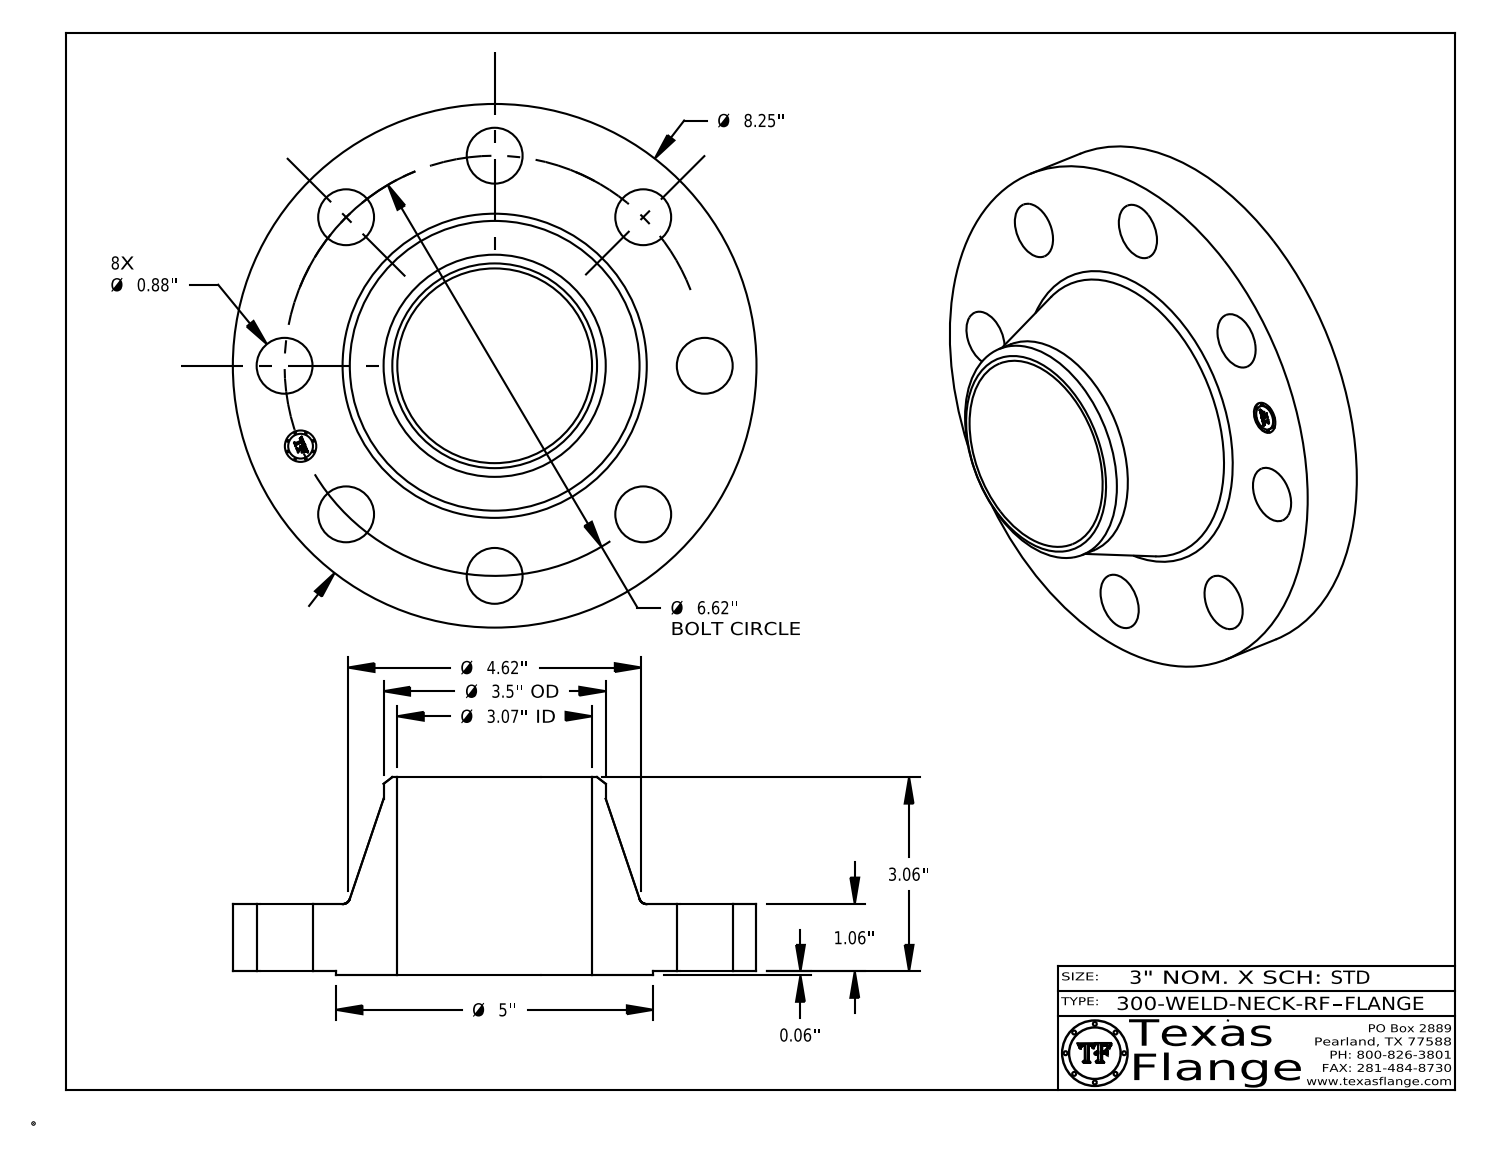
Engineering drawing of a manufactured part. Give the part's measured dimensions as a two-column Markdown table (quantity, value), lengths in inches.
| quantity | value |
| --- | --- |
| part name | 300-WELD-NECK-RF |
| STEP written by | CATIA V5 STEP AP214 (AUTOMOTIVE_DESIGN) |
| units | inches |
| bodies | 1 solid, 419 faces (369 planar, 44 cylindrical, 6 other) |
| overall size | 8.25 × 8.25 × 3.123 |
| volume | 54.48 in³ |
| surface area | 182.3 in² |
| round holes (diameter × count) | 0.88 × 8, 0.495 × 1, 3.068 × 1 |
| round bosses / shafts (diameter × count) | 0.03 × 8, 8.25 × 1, 5 × 1, 3.5 × 1, 0.39 × 1 |
| main face-to-face distances | 1.06, 0.063, 1.122, 3.122, 3.06, 2, 0.015, 1.107, 1.045, 2.015 |
| hole center spacings | 3.31, 2.533, 6.116, 4.681, 4.681, 1.291, 3.678, 6.493 |
